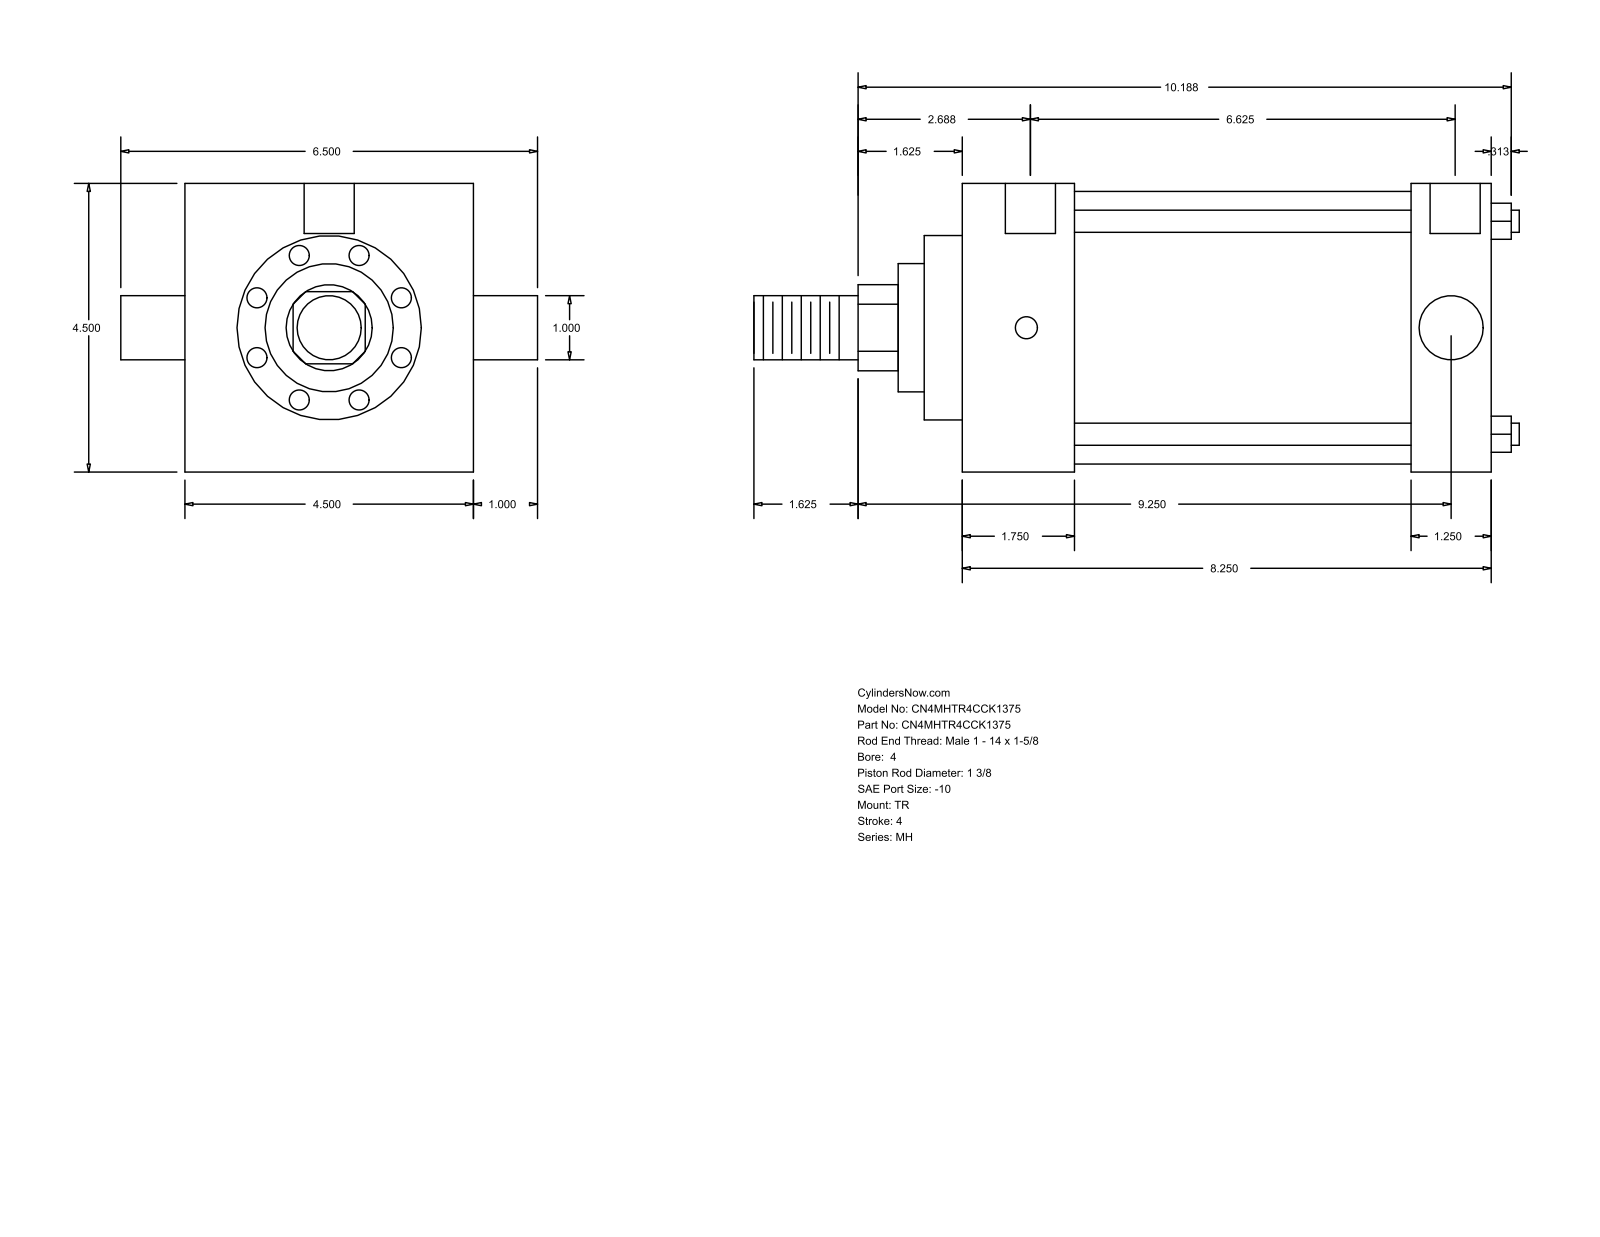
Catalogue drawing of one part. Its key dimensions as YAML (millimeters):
part_name: "MH_TR__0400_1.375"
step_written_by: "GSSL Pune (CONFIG_CONTROL_DESIGN)"
units: millimeters
bodies: {solids: 0, faces: 86, planar: 61, cylindrical: 25, other: 0}
overall_size: [303.21, 165.1, 114.3]
round_holes:
  - {diameter: 8.73, count: 3}
  - {diameter: 19.84, count: 2}
round_bosses_or_shafts:
  - {diameter: 8.76, count: 4}
  - {diameter: 25.4, count: 2}
  - {diameter: 107.95, count: 1}
  - {diameter: 73.03, count: 1}
  - {diameter: 50.8, count: 1}
  - {diameter: 34.92, count: 1}
partial_cylinders:
  - {radius: 17.06, count: 1}
face_to_face_distances: [114.3, 209.55, 165.1, 44.45, 177.8, 133.35, 31.75, 15.08, 59.53, 192.88]
hole_center_spacings: [1.58, 1.59, 168.28, 169.86, 169.87, 171.45]
